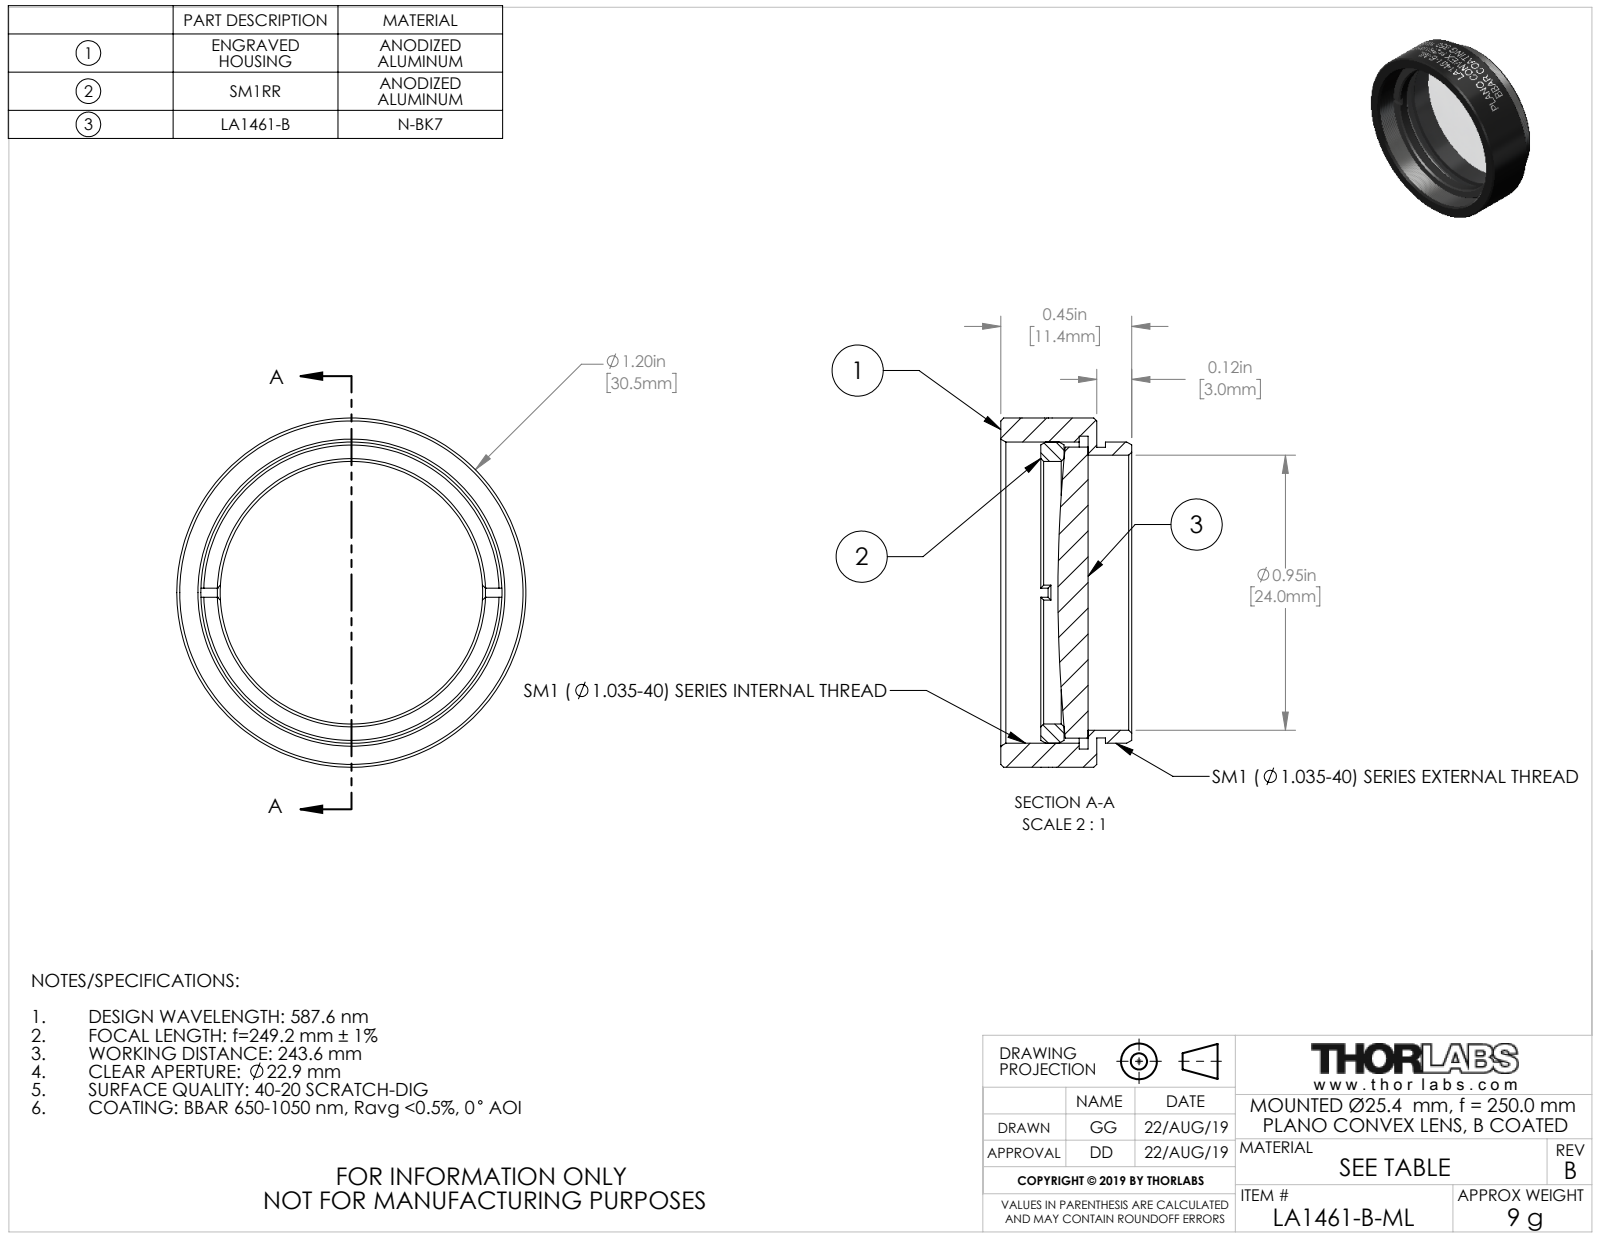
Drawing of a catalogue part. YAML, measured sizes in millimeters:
part_name: "24436-E0W"
step_written_by: "SolidWorks 2018 (CONFIG_CONTROL_DESIGN)"
units: millimeters
bodies: {solids: 3, faces: 155, planar: 20, cylindrical: 111, other: 24}
overall_size: [30.48, 30.48, 11.43]
volume: 3250
surface_area: 4313
round_holes:
  - {diameter: 22.91, count: 1}
  - {diameter: 24, count: 1}
  - {diameter: 27.3, count: 1}
round_bosses_or_shafts:
  - {diameter: 30.48, count: 1}
  - {diameter: 26.29, count: 1}
  - {diameter: 25.4, count: 1}
  - {diameter: 25.37, count: 1}
face_to_face_distances: [0.76, 8.38, 7.62, 2.85, 2.09, 5.53, 4.88, 4.12, 2.03, 3.5]
